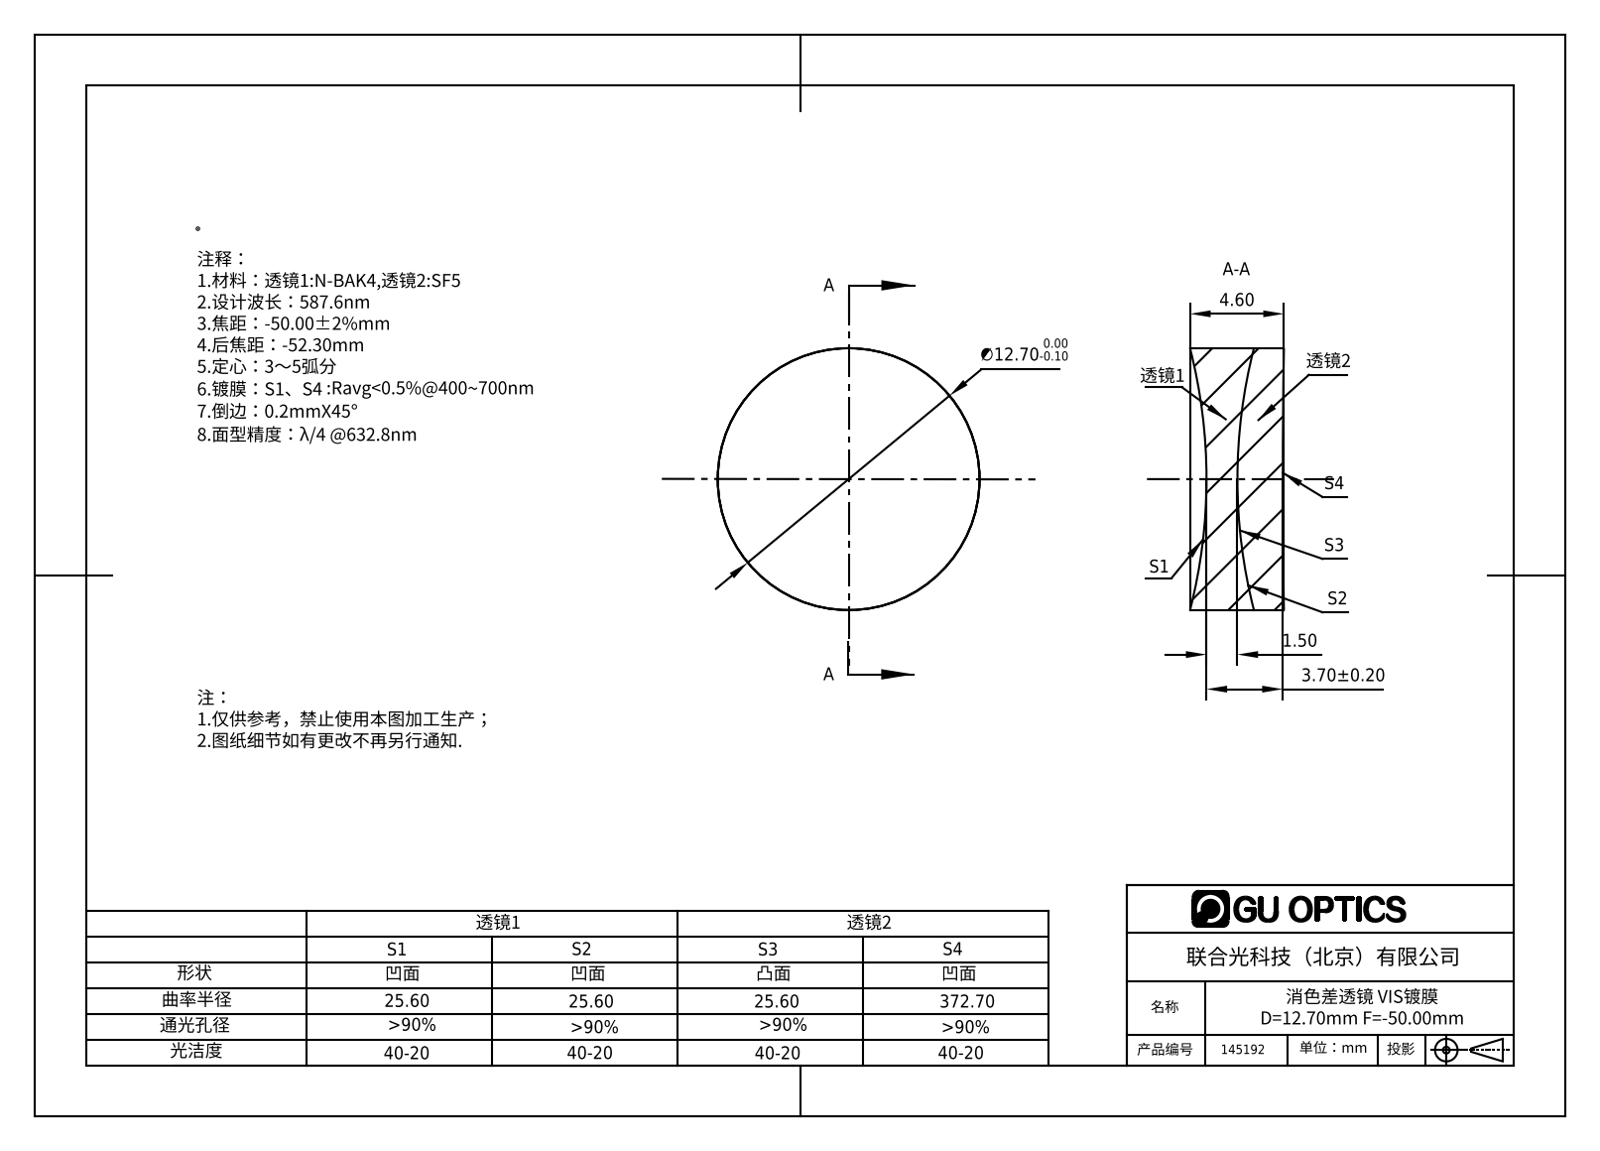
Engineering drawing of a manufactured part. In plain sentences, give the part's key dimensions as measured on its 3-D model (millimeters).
The part is named "145192". Its 3-D file was written by "SolidWorks 2016 (AUTOMOTIVE_DESIGN)". It is 2 solids with 12 faces: 0 planar, 4 cylindrical and 8 other. Overall it measures 12.7 by 12.7 by 4.55 millimeters. Its volume is 523 cubic millimeters and its surface area 694 square millimeters. Round bosses or shafts: 1 of diameter 12.7.
